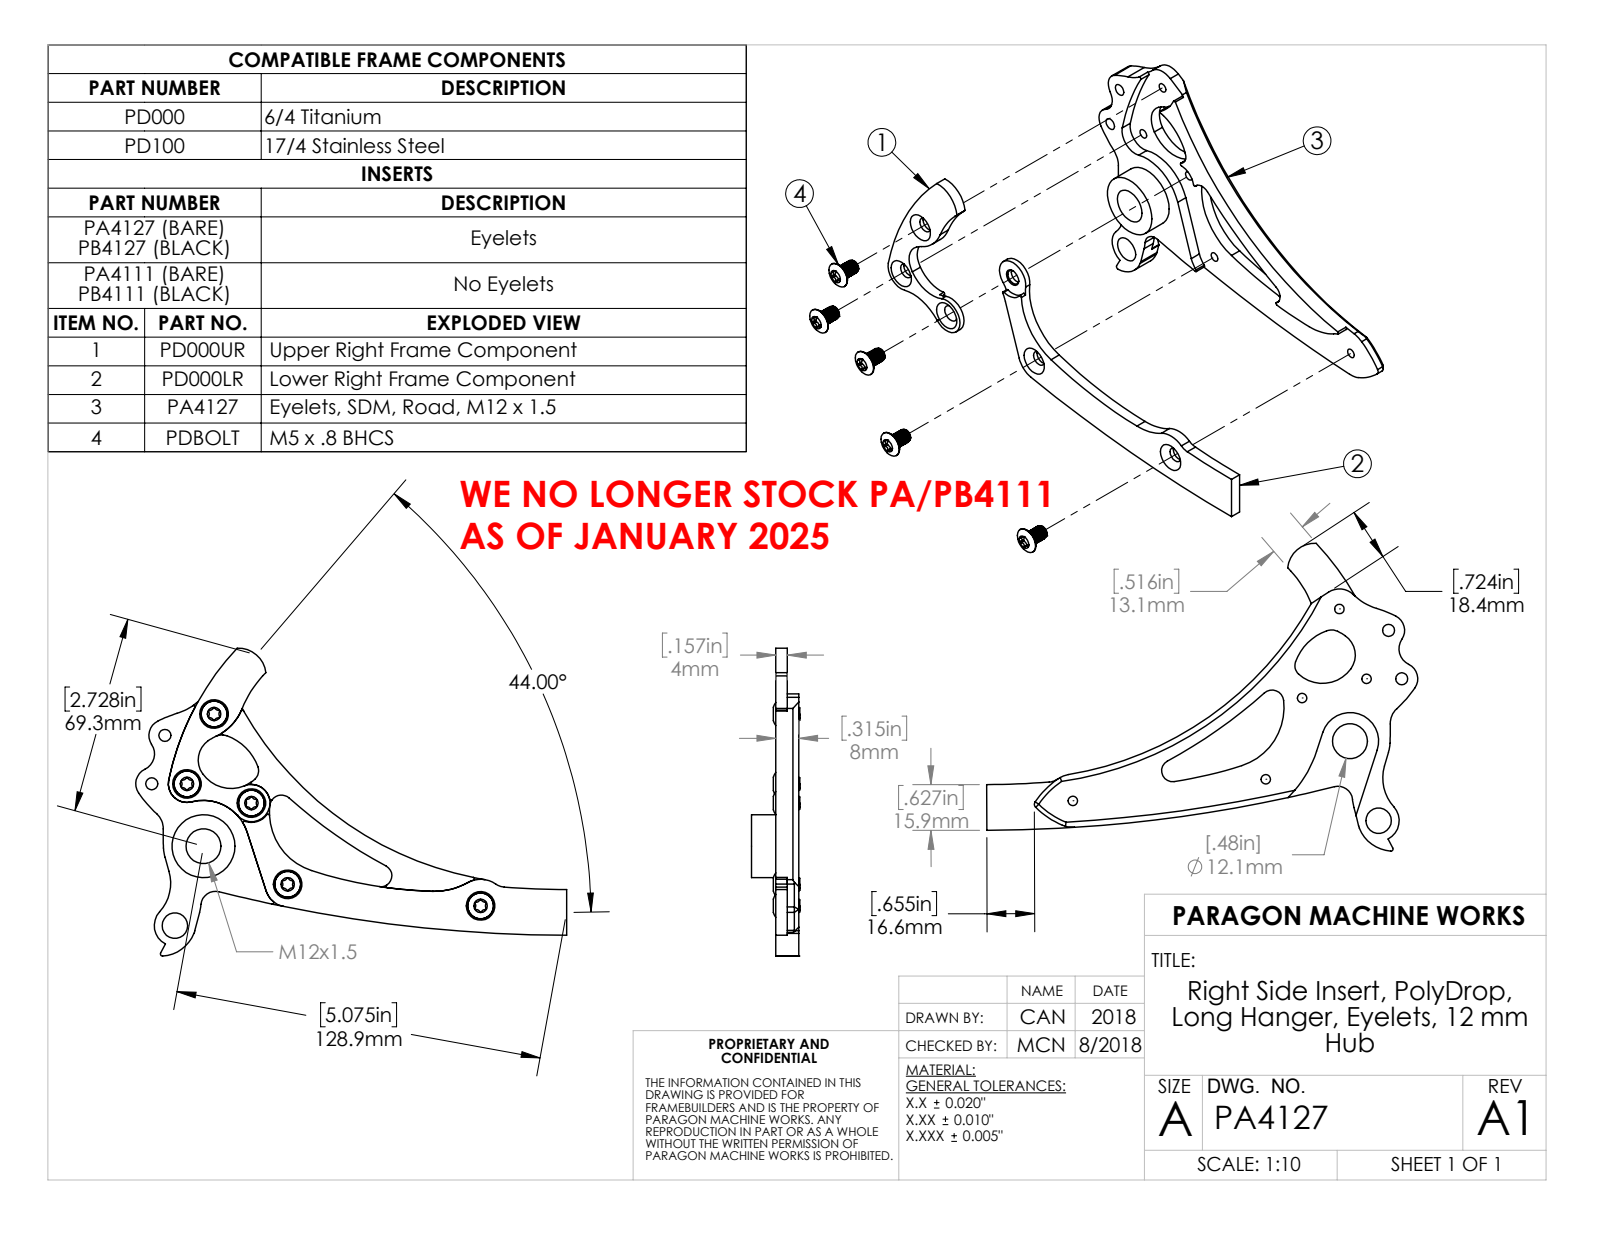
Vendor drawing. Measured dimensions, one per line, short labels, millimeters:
name: PA4127
written by: SolidWorks 2018 (AUTOMOTIVE_DESIGN)
unit: mm
bodies: 1 solid, 104 faces (13 planar, 85 cylindrical, 6 other)
size: 133.88 × 91.51 × 16.5
volume: 25 059 mm³; area: 14 067 mm²
holes: 5× ⌀3.3, 2× ⌀4.2, 1× ⌀8.9, 1× ⌀12.2
bosses: 1× ⌀22
rounds: 9× R0.5, 2× R5.59, 2× R6.5, 2× R7, 2× R18, 2× R20, 2× R30.71, 2× R44.03
face distances: 4, 8, 3.5, 0.5, 4.5, 16.5, 13, 12.5, 8.5, 26
hole spacings: 22.5, 49.67, 12.3, 17.5, 18.6, 18.73, 23.48, 26.16
